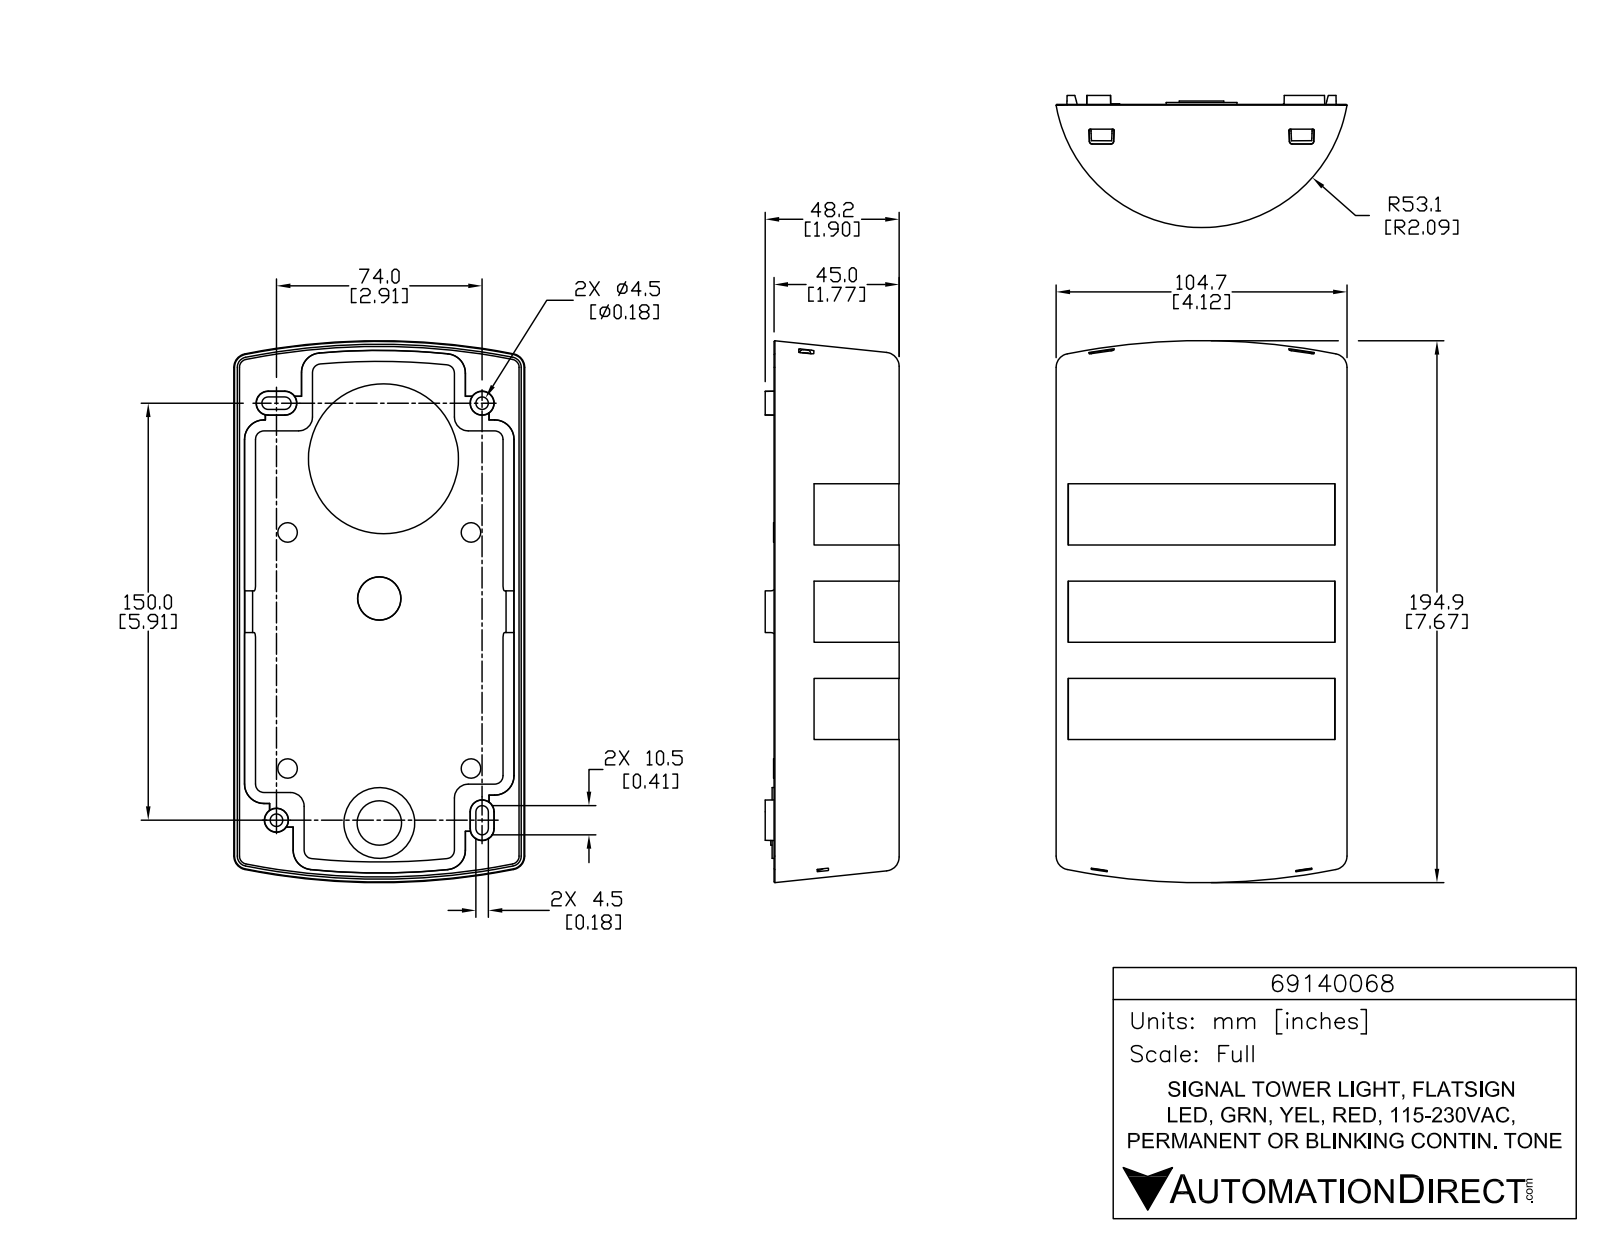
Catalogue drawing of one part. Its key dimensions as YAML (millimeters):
part_name: "69140068"
step_written_by: "SolidWorks 2017 (AUTOMOTIVE_DESIGN)"
units: millimeters
bodies: {solids: 1, faces: 1074, planar: 520, cylindrical: 128, other: 426}
overall_size: [194.9, 104.7, 48.3]
volume: 628600
surface_area: 59790
round_holes:
  - {diameter: 2.3, count: 1}
round_bosses_or_shafts:
  - {diameter: 54, count: 1}
  - {diameter: 25.5, count: 1}
  - {diameter: 16, count: 1}
  - {diameter: 13.1, count: 1}
  - {diameter: 3.3, count: 1}
partial_cylinders:
  - {radius: 1, count: 12}
  - {radius: 0.3, count: 4}
  - {radius: 0.2, count: 3}
  - {radius: 0.2, count: 2}
  - {radius: 0.5, count: 2}
  - {radius: 0.5, count: 2}
  - {radius: 0.5, count: 2}
  - {radius: 0.5, count: 2}
face_to_face_distances: [0.8, 2, 1.2, 2.8, 1.6, 4, 1, 0.5, 3.5, 3]
